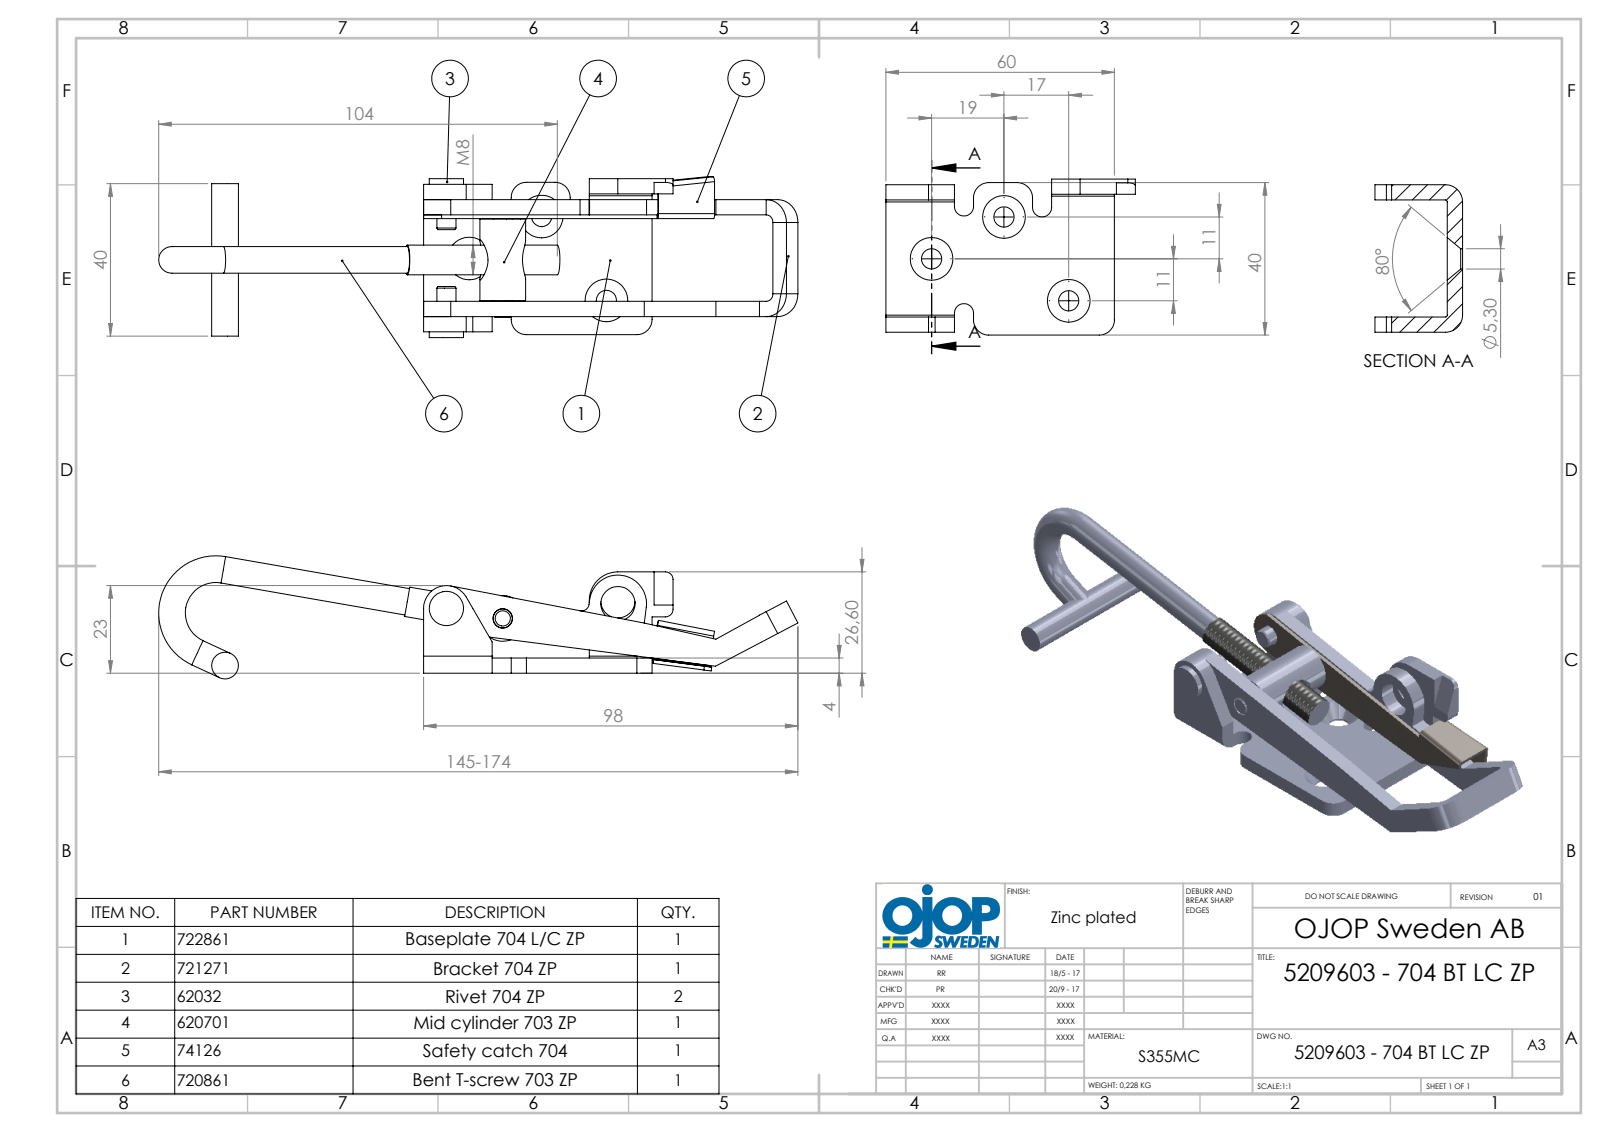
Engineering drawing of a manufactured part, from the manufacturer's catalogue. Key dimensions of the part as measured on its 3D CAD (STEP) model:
Part name (STEP PRODUCT): 5209603 - 704 BT LC ZP; 74086 - Böjd T-skruv 703 RF; 704 - Safety Catch; 704 - Mid Cylinder (+3 more)
STEP written by: SolidWorks 2015 (AUTOMOTIVE_DESIGN)
Units: millimetres
Bodies: 7 solids, 219 faces (103 planar, 94 cylindrical, 22 other)
Overall size (bounding box): 167.8 × 42.24 × 32.3
Volume: 29 743 mm³ · Surface area: 21 947 mm²
Round holes (diameter × count): ⌀5.3 ×3, ⌀5.1 ×2, ⌀9 ×2, ⌀5.4 ×1, ⌀7.2 ×1, ⌀7.7 ×1
Round bosses / shafts (diameter × count): ⌀7 ×4, ⌀5 ×2, ⌀12 ×1, ⌀9 ×1, ⌀7.8 ×1
Partial cylindrical surfaces — rounded edges, fillets, slot ends (radius × count): R2 ×5, R4 ×4, R0.3 ×3, R0.5 ×3, R1.3 ×3, R2.5 ×3, R4.5 ×3, R6 ×3
Main face-to-face distances: 4, 26.7, 30.7, 1, 22.7, 5.5, 32.2, 36.2, 5, 21.7
Hole centre spacings: 0.74, 15.02, 21.95, 27.8, 30.49, 30.56, 37.64, 45.04
